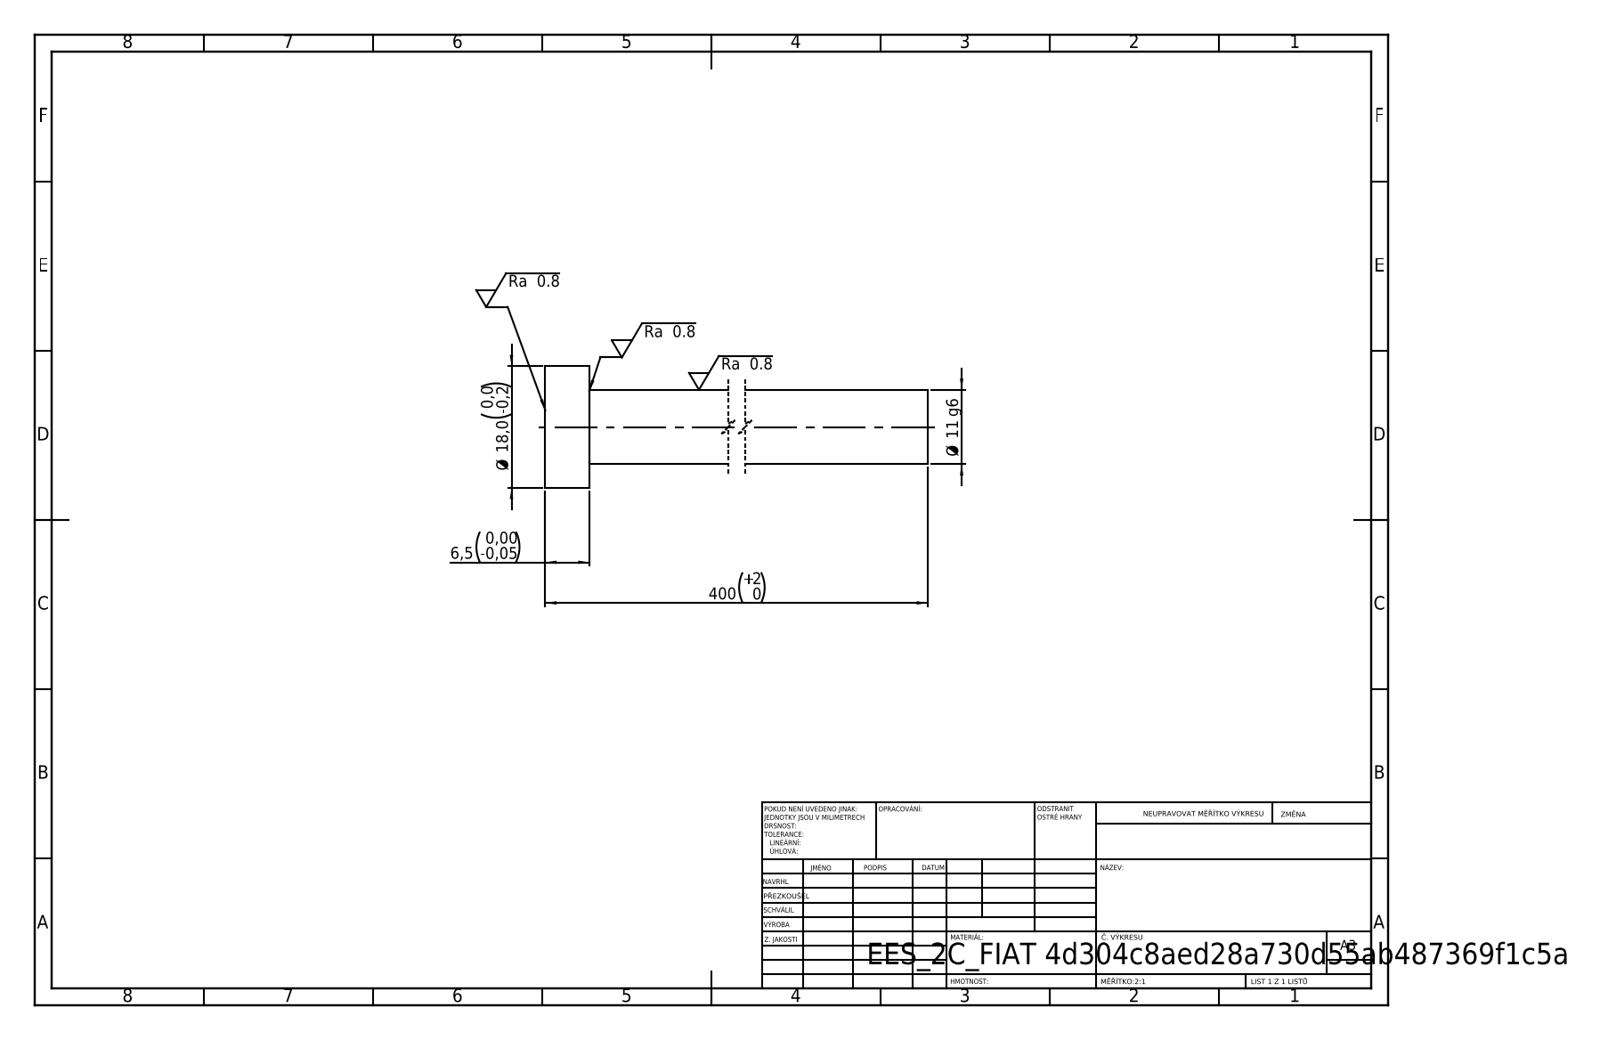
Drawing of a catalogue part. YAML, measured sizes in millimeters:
step_written_by: "SolidWorks 2019 (CONFIG_CONTROL_DESIGN)"
units: millimeters
bodies: {solids: 1, faces: 7, planar: 3, cylindrical: 4, other: 0}
overall_size: [400, 18, 18]
volume: 39050
surface_area: 14475
round_bosses_or_shafts:
  - {diameter: 18, count: 1}
  - {diameter: 11, count: 1}
face_to_face_distances: [6.5, 400, 393.5]
